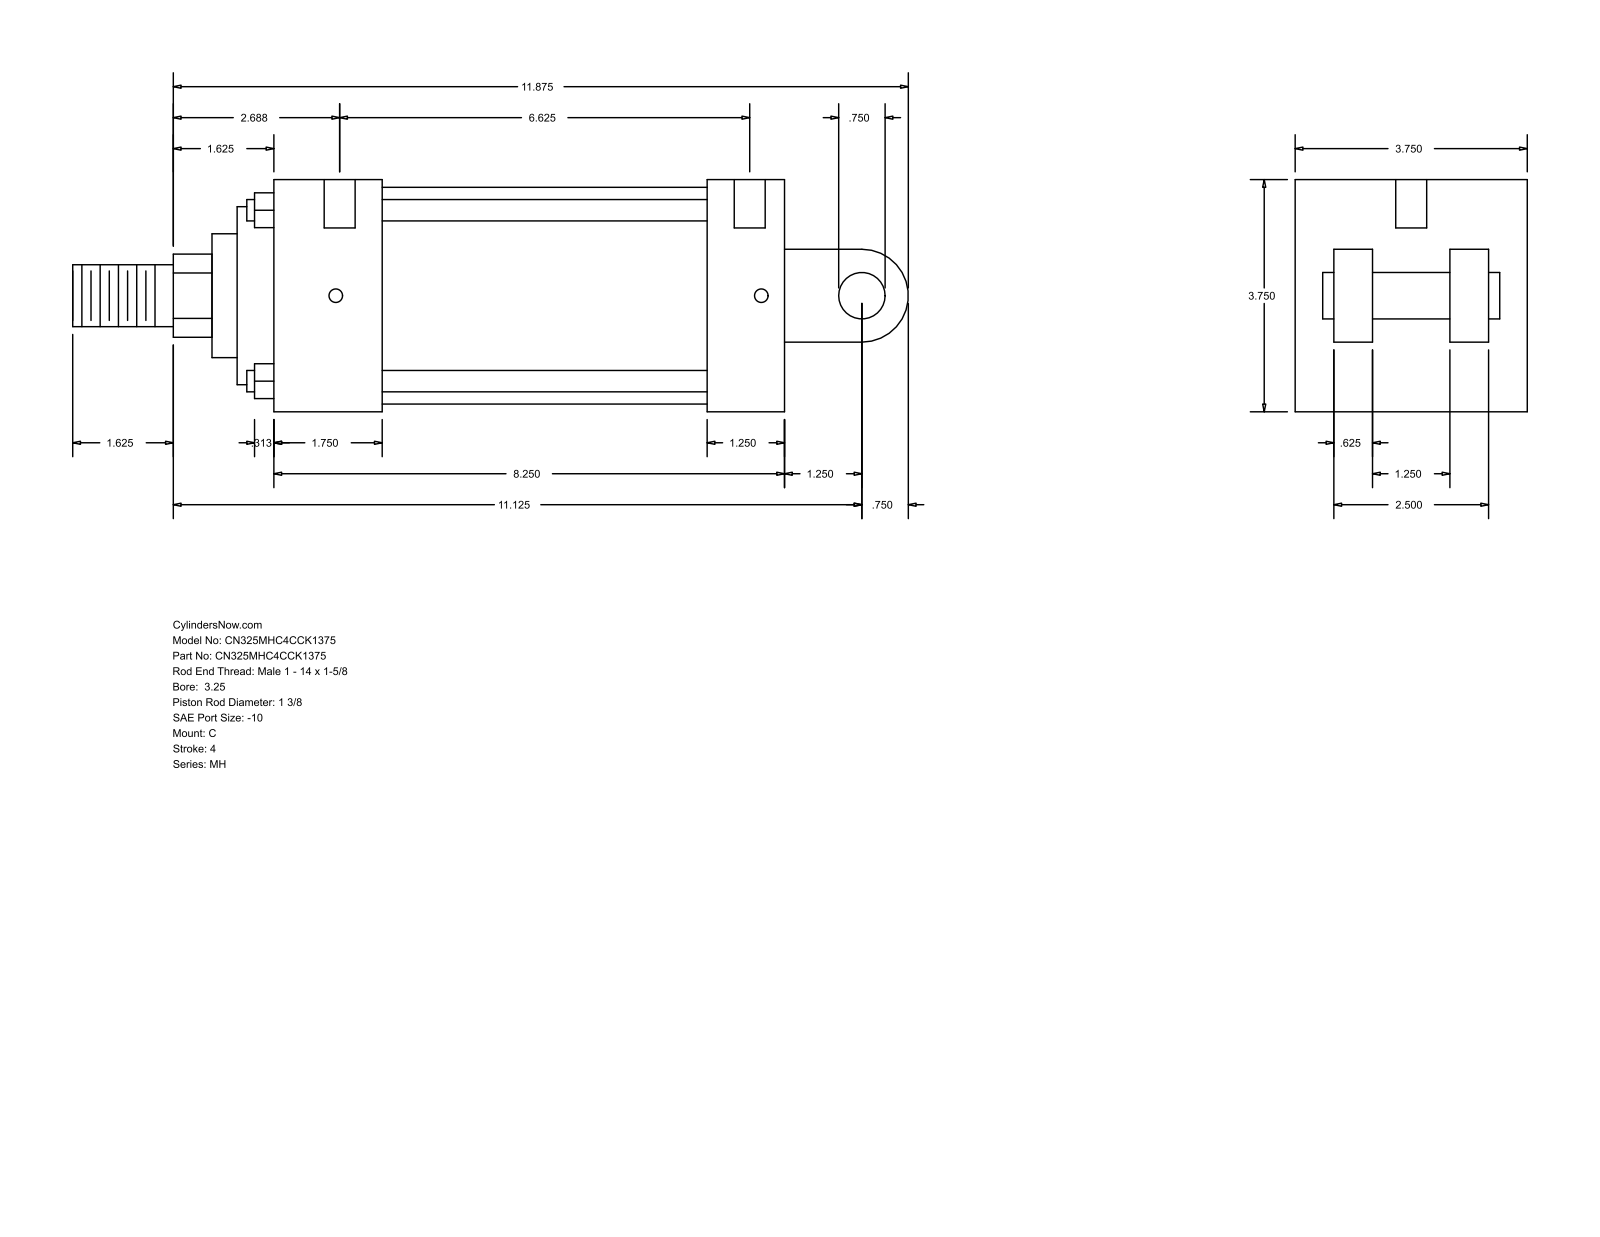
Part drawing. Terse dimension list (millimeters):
name: MH_C__0325_1.375
written by: GSSL Pune (CONFIG_CONTROL_DESIGN)
unit: mm
bodies: 0 solids, 101 faces (71 planar, 30 cylindrical, 0 other)
size: 342.9 × 95.25 × 95.25
holes: 4× ⌀5.56, 2× ⌀12.7
bosses: 4× ⌀8.76, 1× ⌀88.9, 1× ⌀73.03, 1× ⌀50.8, 1× ⌀34.92, 1× ⌀25.4, 1× ⌀19.05
rounds: 1× R17.06, 1× R19.05
face distances: 95.24, 15.87, 63.5, 209.55, 79.37, 31.74, 47.63, 44.45, 177.8, 133.35
hole spacings: 174.63, 1.59, 4.76, 168.28, 169.87, 173.04
